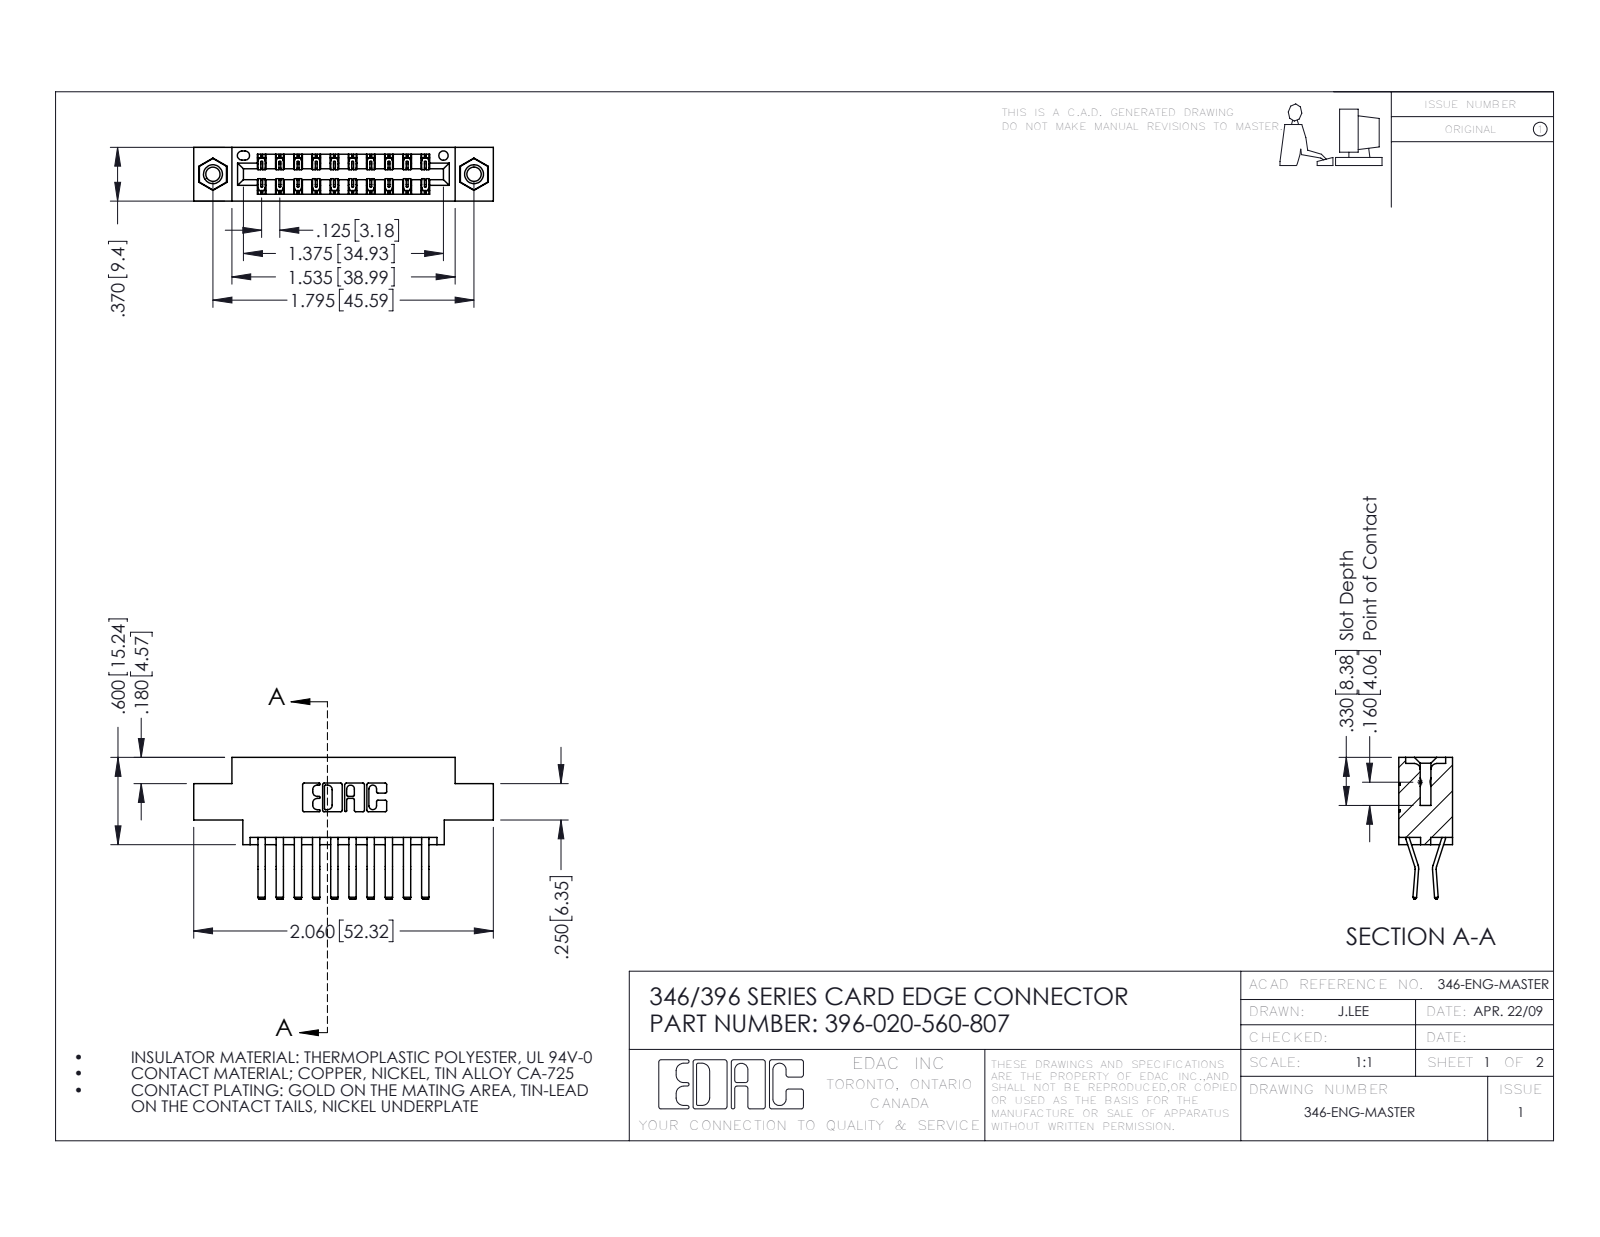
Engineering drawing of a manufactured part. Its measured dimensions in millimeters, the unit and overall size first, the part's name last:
Units: millimetres
Overall size (bounding box): 52.3 × 24.8 × 9.4
Round holes (diameter × count): ⌀2.5 ×2, ⌀3.2 ×2, ⌀4 ×2, ⌀1.6 ×1
Round bosses / shafts (diameter × count): ⌀3.9 ×2
Partial cylindrical surfaces — rounded edges, fillets, slot ends (radius × count): R0.2 ×30, R0.3 ×22, R0.2 ×6, R0.8 ×6, R0.7 ×3, R0.3 ×2, R0.4 ×2, R0.6 ×2
Main face-to-face distances: 6.4, 9.4, 1.2, 8.2, 0.6, 5.6, 3.8, 1.8, 7.6, 7
Hole centre spacings: 6.2, 40.4, 45.6
Volume: 4 820 mm³ · Surface area: 6 684 mm²
Bodies: 23 solids, 1266 faces (812 planar, 438 cylindrical, 16 other)
Part name (STEP PRODUCT): 345-292-001_560 Tail; 346 Part_0.170 Offset - 0.156 Dia-TI; 396-020-560-807; 345-250-001_345-250-005-103
STEP written by: SolidWorks 2016 (CONFIG_CONTROL_DESIGN)
